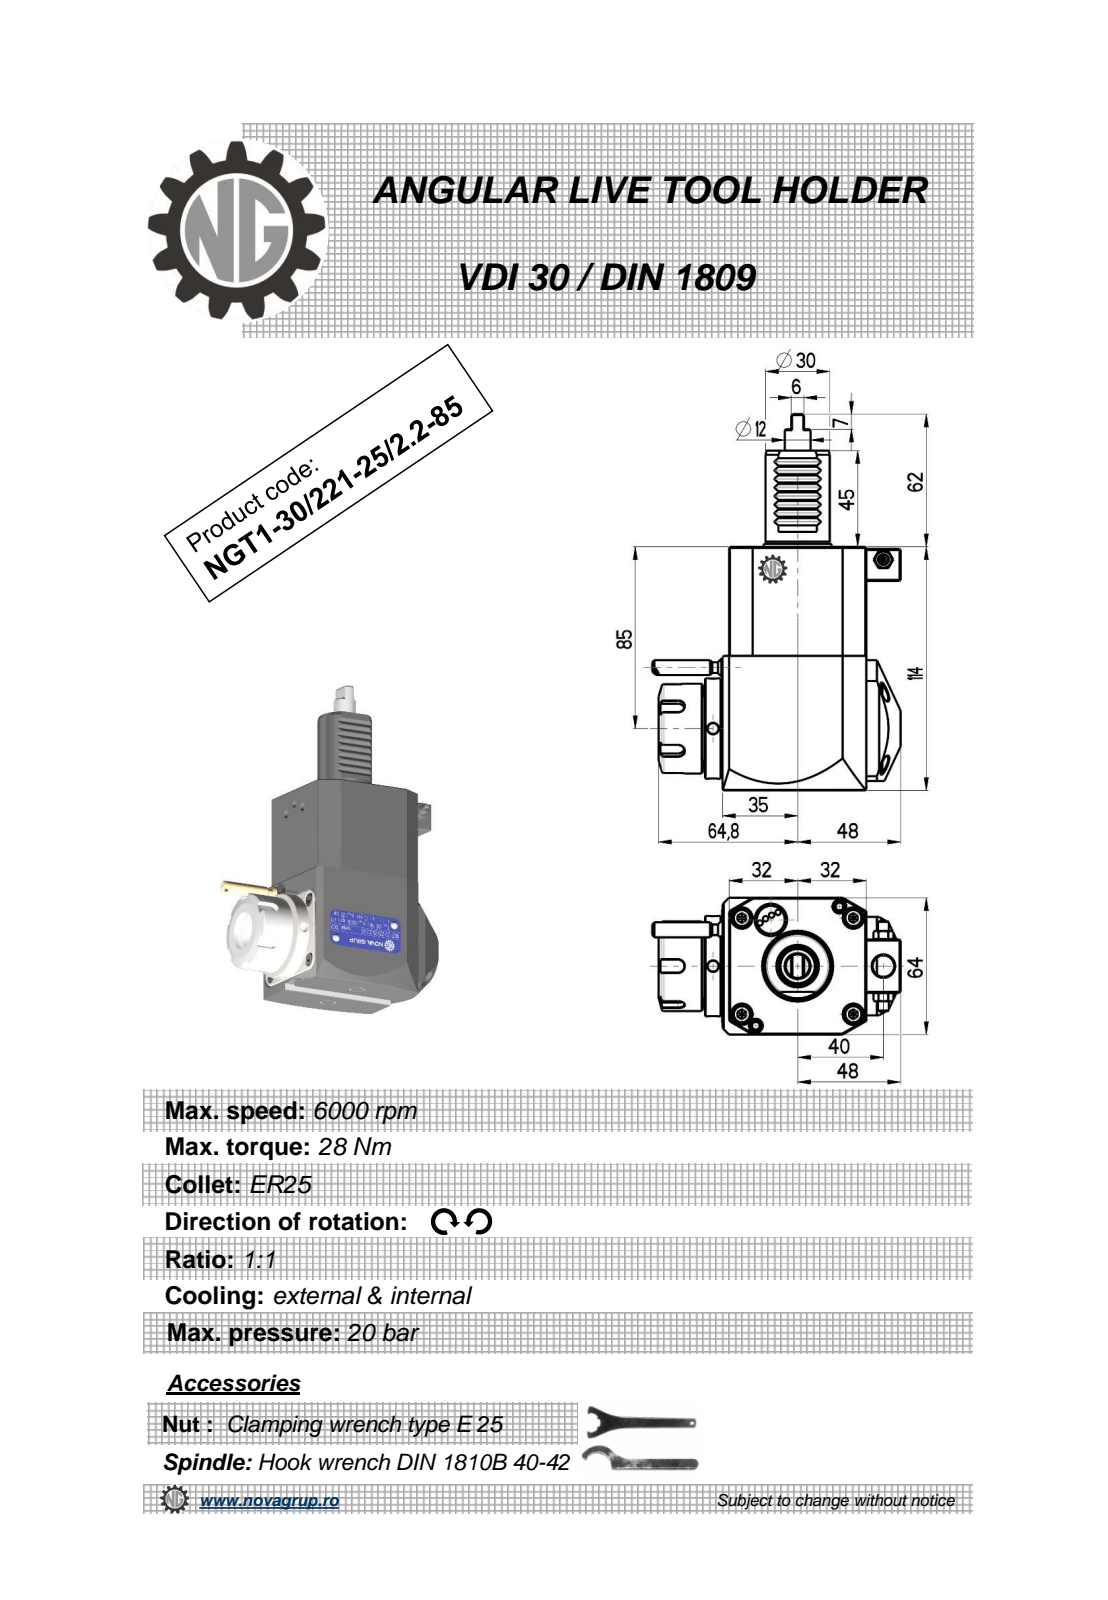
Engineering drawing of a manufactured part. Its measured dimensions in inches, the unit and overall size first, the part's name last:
Units: inches
Overall size (bounding box): 6.929 × 4.659 × 2.52
Round holes (diameter × count): ⌀0.197 ×2, ⌀0.098 ×1, ⌀0.118 ×1, ⌀0.165 ×1, ⌀0.374 ×1, ⌀0.394 ×1, ⌀0.799 ×1
Round bosses / shafts (diameter × count): ⌀0.353 ×2, ⌀0.197 ×2, ⌀1.85 ×1, ⌀1.654 ×1, ⌀1.433 ×1, ⌀1.299 ×1, ⌀1.181 ×1, ⌀0.472 ×1
Partial cylindrical surfaces — rounded edges, fillets, slot ends (radius × count): R0.01 ×12, R0.012 ×8, R0.118 ×5, R0.031 ×2, R6.299 ×2, R1.216 ×1
Main face-to-face distances: 2.52, 4.488, 3.009, 0.126, 2.646, 2.638, 0.02, 0.118, 0.315, 0.295
Hole centre spacings: 1.307, 2.005, 3.012, 3.128, 4.411
Volume: 34.99 in³ · Surface area: 83.09 in²
Bodies: 1 solid, 409 faces (183 planar, 84 cylindrical, 142 other)
Part name (STEP PRODUCT): NGT1_30_221_25_2_2_85
STEP written by: PRO/ENGINEER BY PARAMETRIC TECHNOLOGY CORPORATION, 2010280 (CONFIG_CONTROL_DESIGN)
